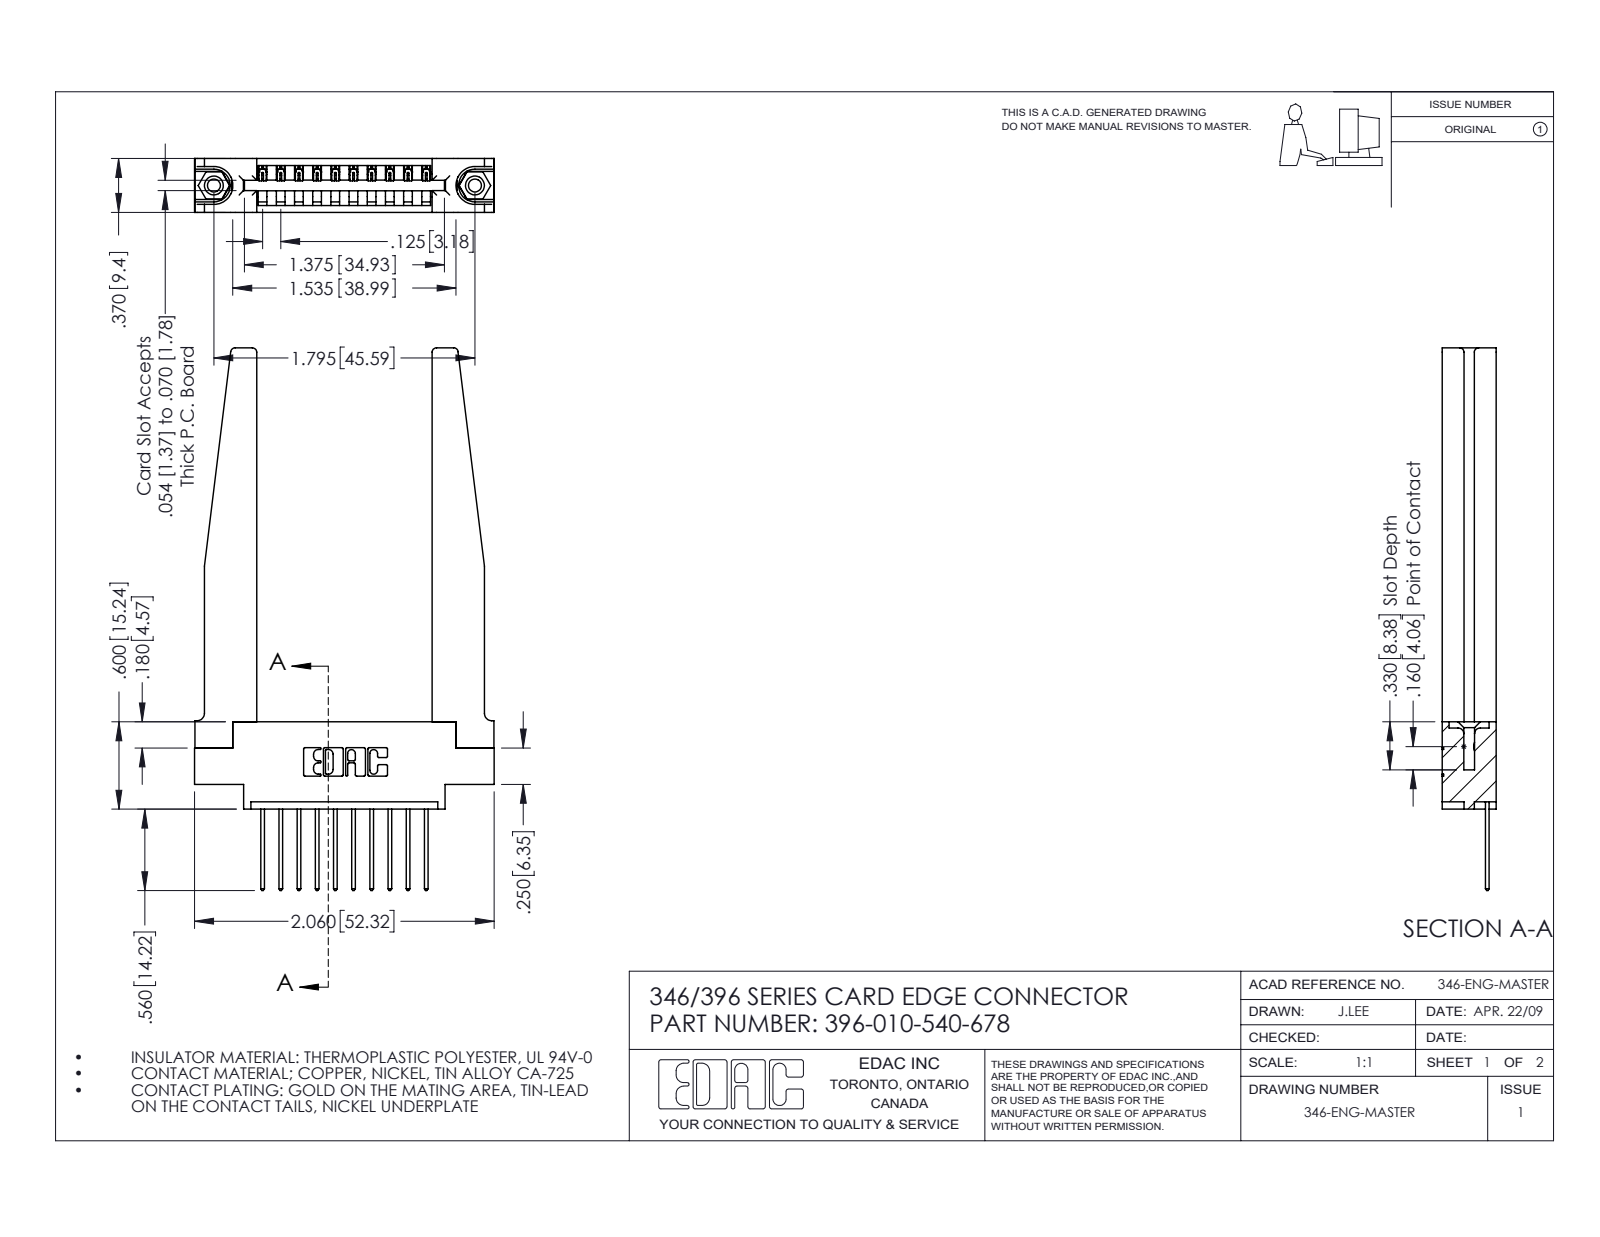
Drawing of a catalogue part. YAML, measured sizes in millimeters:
part_name: "396-010-540-678; 345-250-001_345-250-001-102; 346-220-078_345-220-078; 345-292-001_345-293-140 (+1 more)"
step_written_by: "SolidWorks 2016 (CONFIG_CONTROL_DESIGN)"
units: millimeters
bodies: {solids: 15, faces: 940, planar: 622, cylindrical: 266, other: 52}
overall_size: [94.7, 52.3, 9.4]
volume: 11600
surface_area: 12260
round_holes:
  - {diameter: 2.3, count: 2}
  - {diameter: 3.2, count: 2}
  - {diameter: 4, count: 2}
  - {diameter: 1.6, count: 1}
round_bosses_or_shafts:
  - {diameter: 3.9, count: 2}
partial_cylinders:
  - {radius: 0.3, count: 22}
  - {radius: 0.2, count: 20}
  - {radius: 0.3, count: 20}
  - {radius: 0.8, count: 8}
  - {radius: 0.2, count: 6}
  - {radius: 0.8, count: 6}
  - {radius: 0.7, count: 3}
  - {radius: 0.8, count: 2}
face_to_face_distances: [9.4, 3.8, 3.8, 1.8, 1.2, 8.2, 6.4, 5.6, 2.6, 4.4]
hole_center_spacings: [6.2, 40.4, 45.6]
